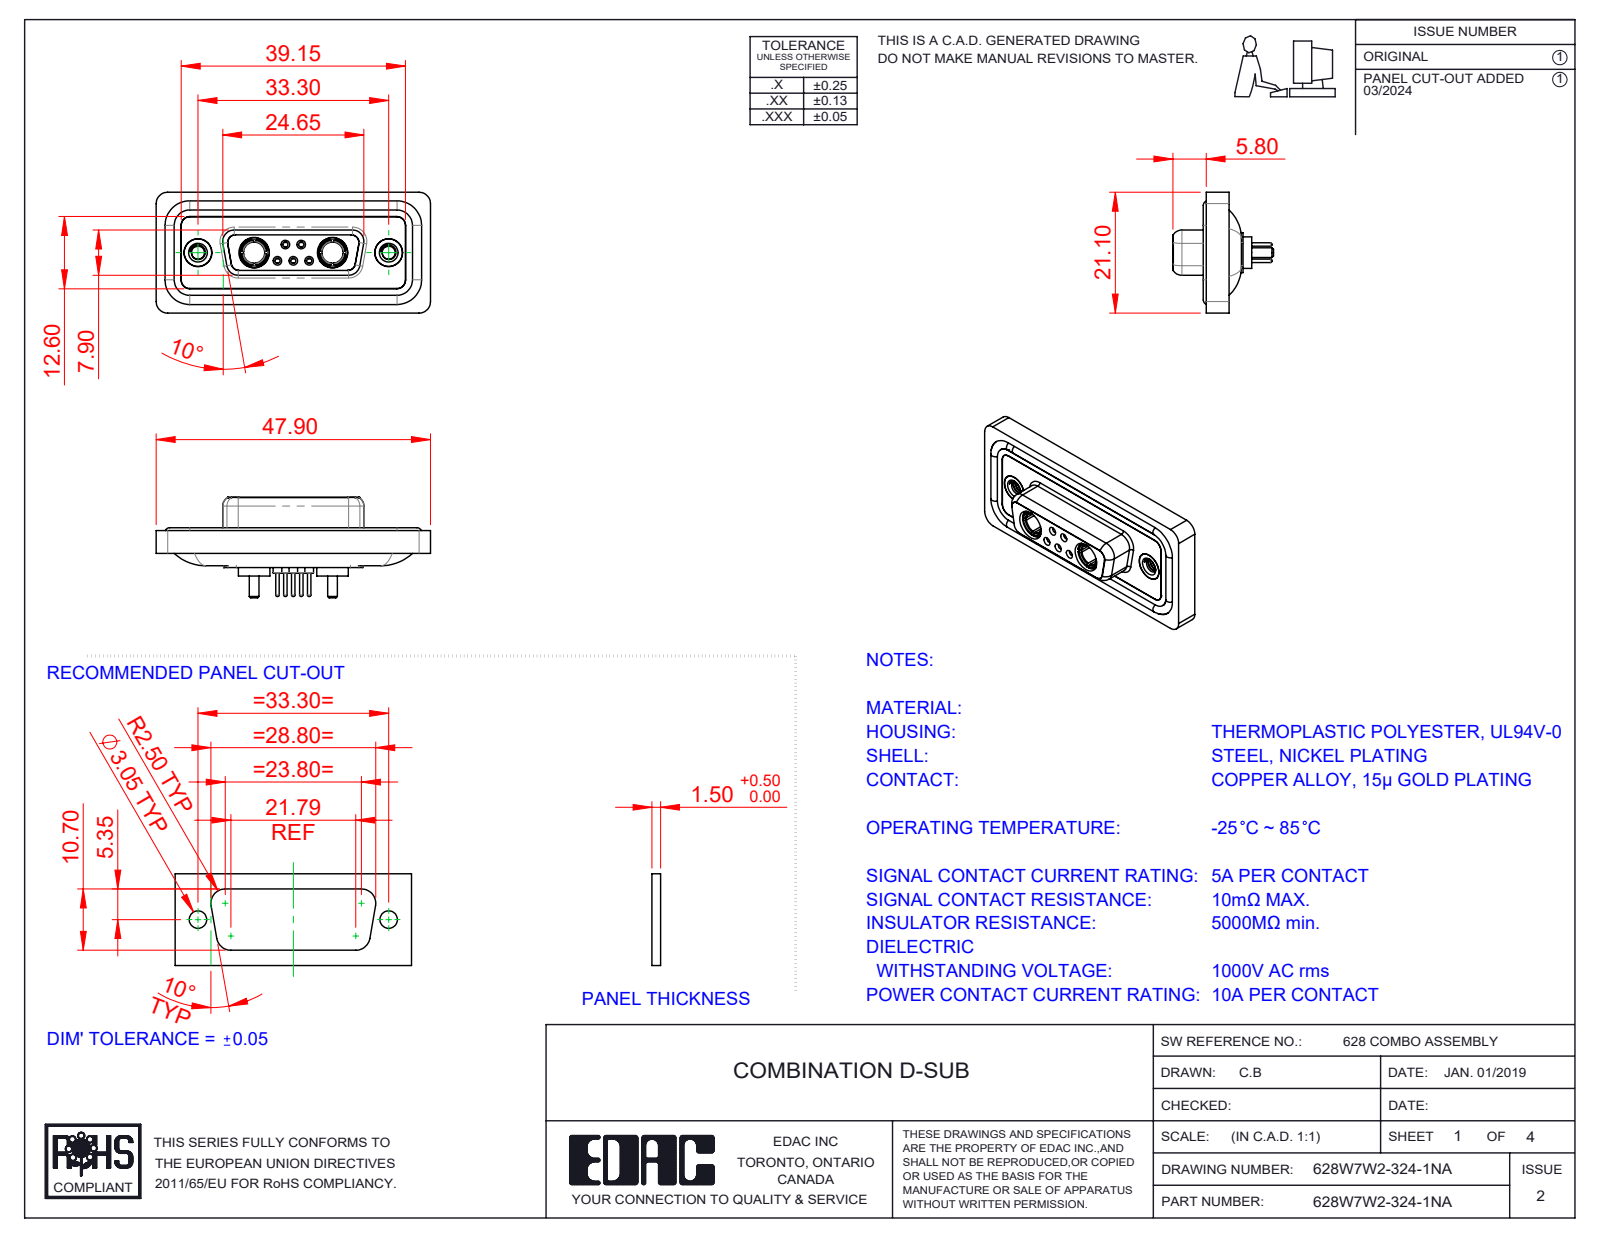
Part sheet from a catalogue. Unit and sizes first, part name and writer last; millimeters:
Units: millimetres
Overall size (bounding box): 47.9 × 21.1 × 17.55
Round holes (diameter × count): ⌀0.9 ×5, ⌀1.1 ×5, ⌀1.5 ×5, ⌀2 ×5, ⌀4.85 ×4, ⌀1.6 ×3, ⌀1.7 ×2, ⌀2.26 ×2, ⌀3.7 ×2, ⌀4 ×2, ⌀4.05 ×2, ⌀5 ×2
Round bosses / shafts (diameter × count): ⌀1.6 ×6, ⌀2.2 ×5, ⌀0.6 ×5, ⌀5.5 ×2, ⌀5.2 ×2, ⌀4.96 ×2, ⌀4.95 ×2, ⌀4.8 ×2
Partial cylindrical surfaces — rounded edges, fillets, slot ends (radius × count): R1.5 ×22, R2 ×20, R1.35 ×12, R1.6 ×8, R0.25 ×4, R0.5 ×4, R0.6 ×4, R0.65 ×4
Main face-to-face distances: 0.4, 1.8, 1.6, 0.5, 2.9, 1.1, 7.45, 5.65, 6.6, 7.05
Hole centre spacings: 3.16, 2.77, 9.8, 23.5, 4.31, 4.33, 5.03, 5.04
Volume: 6 049 mm³ · Surface area: 9 857 mm²
Bodies: 16 solids, 807 faces (238 planar, 331 cylindrical, 238 other)
Part name (STEP PRODUCT): 628Combo Contact Row 2_24; Power Socket_10A S; 628Combo Shell Rear_15 Contacts; 628Combo Housing_7W2 (+5 more)
STEP written by: SolidWorks 2023 (CONFIG_CONTROL_DESIGN)
